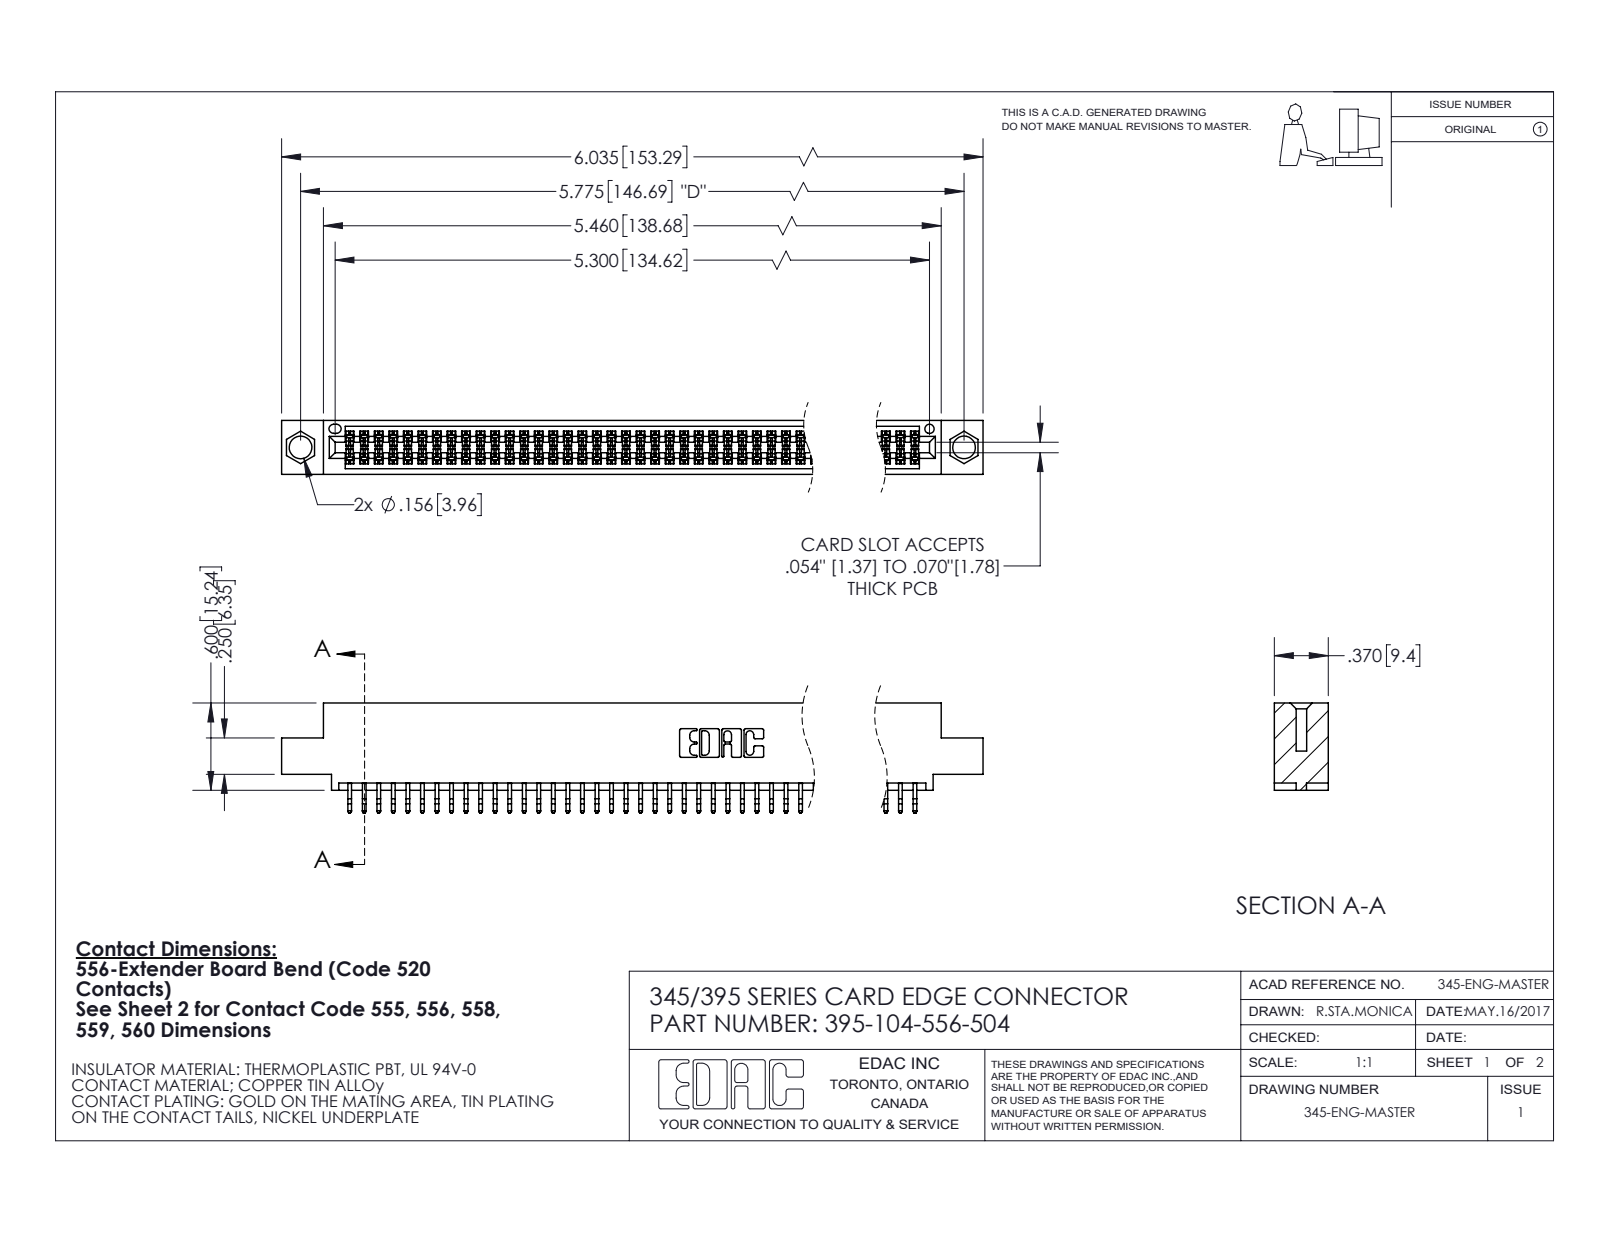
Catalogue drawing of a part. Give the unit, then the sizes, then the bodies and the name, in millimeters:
Units: millimetres
Overall size (bounding box): 153.3 × 19.2 × 9.4
Round holes (diameter × count): ⌀4 ×2, ⌀1.6 ×1
Partial cylindrical surfaces — rounded edges, fillets, slot ends (radius × count): R0.2 ×208, R0.3 ×22, R0.2 ×6, R0.8 ×6, R0.7 ×3, R0.3 ×2, R0.4 ×2, R0.5 ×2
Main face-to-face distances: 7.6, 1.8, 9.4, 5.1, 0.6, 2.5, 6.9, 5.7, 4.4, 3.8
Hole centre spacings: 6.9, 140.7, 146.7
Volume: 14 800 mm³ · Surface area: 21 920 mm²
Bodies: 105 solids, 5968 faces (3946 planar, 2022 cylindrical, 0 other)
Part name (STEP PRODUCT): 395-104-556-504; 345-292-001_556 Tail; 345 Part_0.110 Offset - 0.156 Dia-TI
STEP written by: SolidWorks 2020 (CONFIG_CONTROL_DESIGN)
